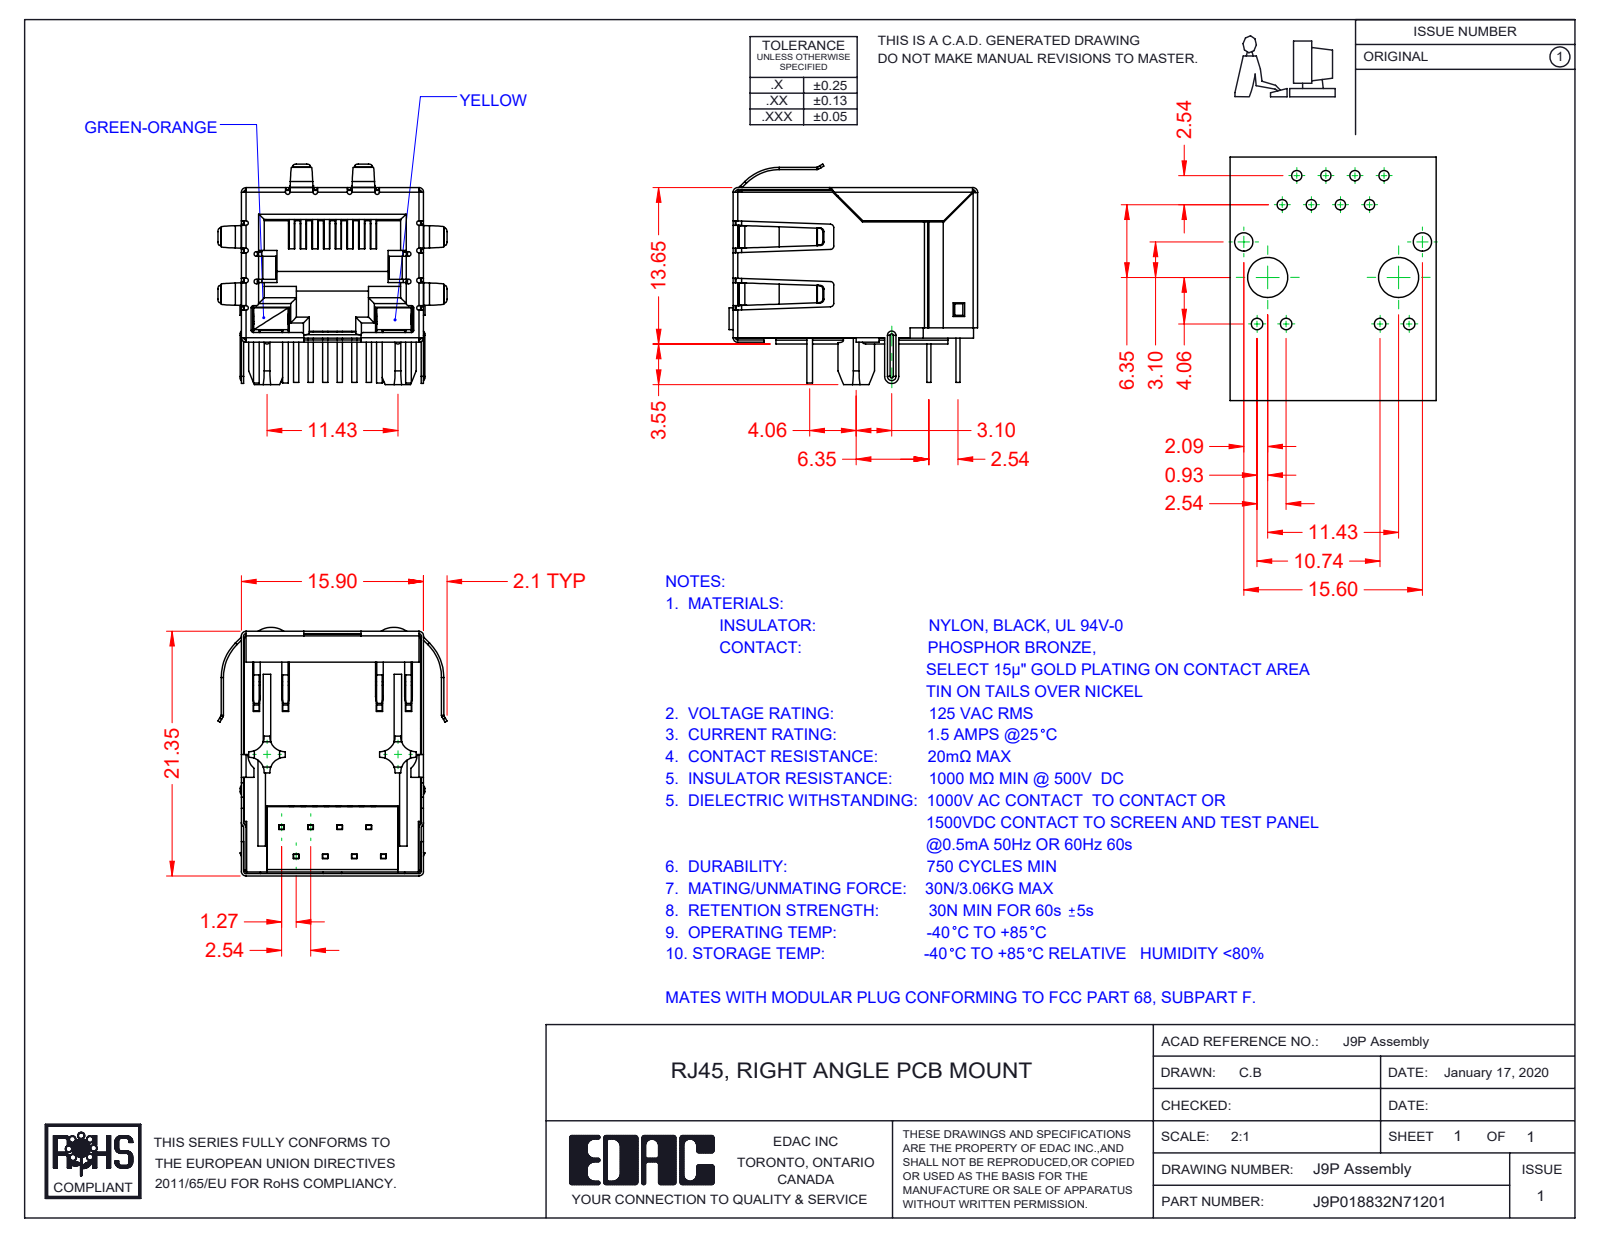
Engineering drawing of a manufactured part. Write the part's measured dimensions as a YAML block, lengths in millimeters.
part_name: "9P-LED LED LH_7-Green-Orange; 9P-LED Insulator; J9P018832N71202; 9P-LED Shield (+4 more)"
step_written_by: "SolidWorks 2016 (CONFIG_CONTROL_DESIGN)"
units: millimeters
bodies: {solids: 13, faces: 1474, planar: 1042, cylindrical: 338, other: 94}
overall_size: [21.7, 20, 19.25]
volume: 2687
surface_area: 7515
partial_cylinders:
  - {radius: 0.2, count: 39}
  - {radius: 0.5, count: 22}
  - {radius: 0.3, count: 20}
  - {radius: 0.4, count: 16}
  - {radius: 1.3, count: 8}
  - {radius: 0.23, count: 5}
  - {radius: 0.11, count: 4}
  - {radius: 0.31, count: 4}
face_to_face_distances: [15.45, 15.7, 15.65, 0.35, 0.54, 15.5, 12.36, 0.6, 1.4, 0.59]
